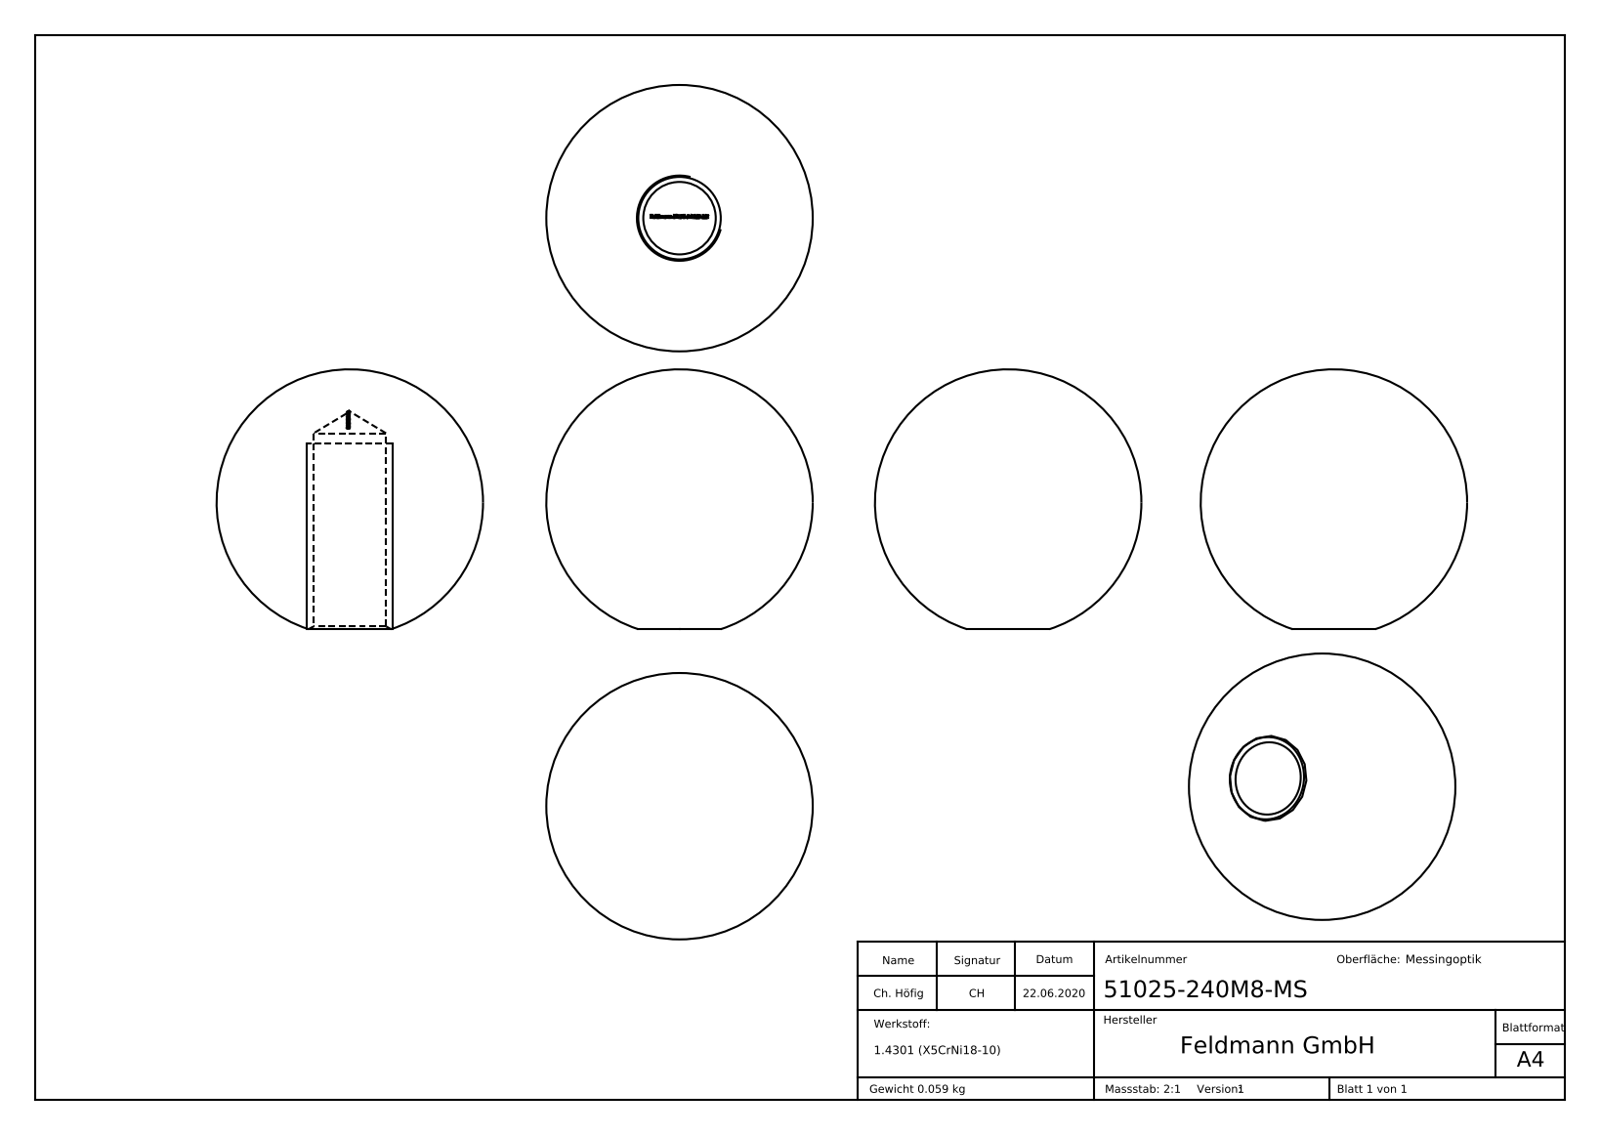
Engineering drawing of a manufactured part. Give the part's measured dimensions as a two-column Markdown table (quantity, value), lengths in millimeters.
| quantity | value |
| --- | --- |
| part name | 51025-240M8-MS |
| STEP written by | SolidWorks 2015 (CONFIG_CONTROL_DESIGN) |
| units | millimeters |
| bodies | 2 solids, 294 faces (133 planar, 1 cylindrical, 160 other) |
| overall size | 25 × 25 × 24.39 |
| volume | 7 473 mm³ |
| surface area | 2 361 mm² |
| round holes (diameter × count) | 6.8 × 1 |
| main face-to-face distances | 0.67, 0.74, 0.77, 0.93, 0.7, 1.02, 1.3, 2.43, 0.31, 1.34 |
